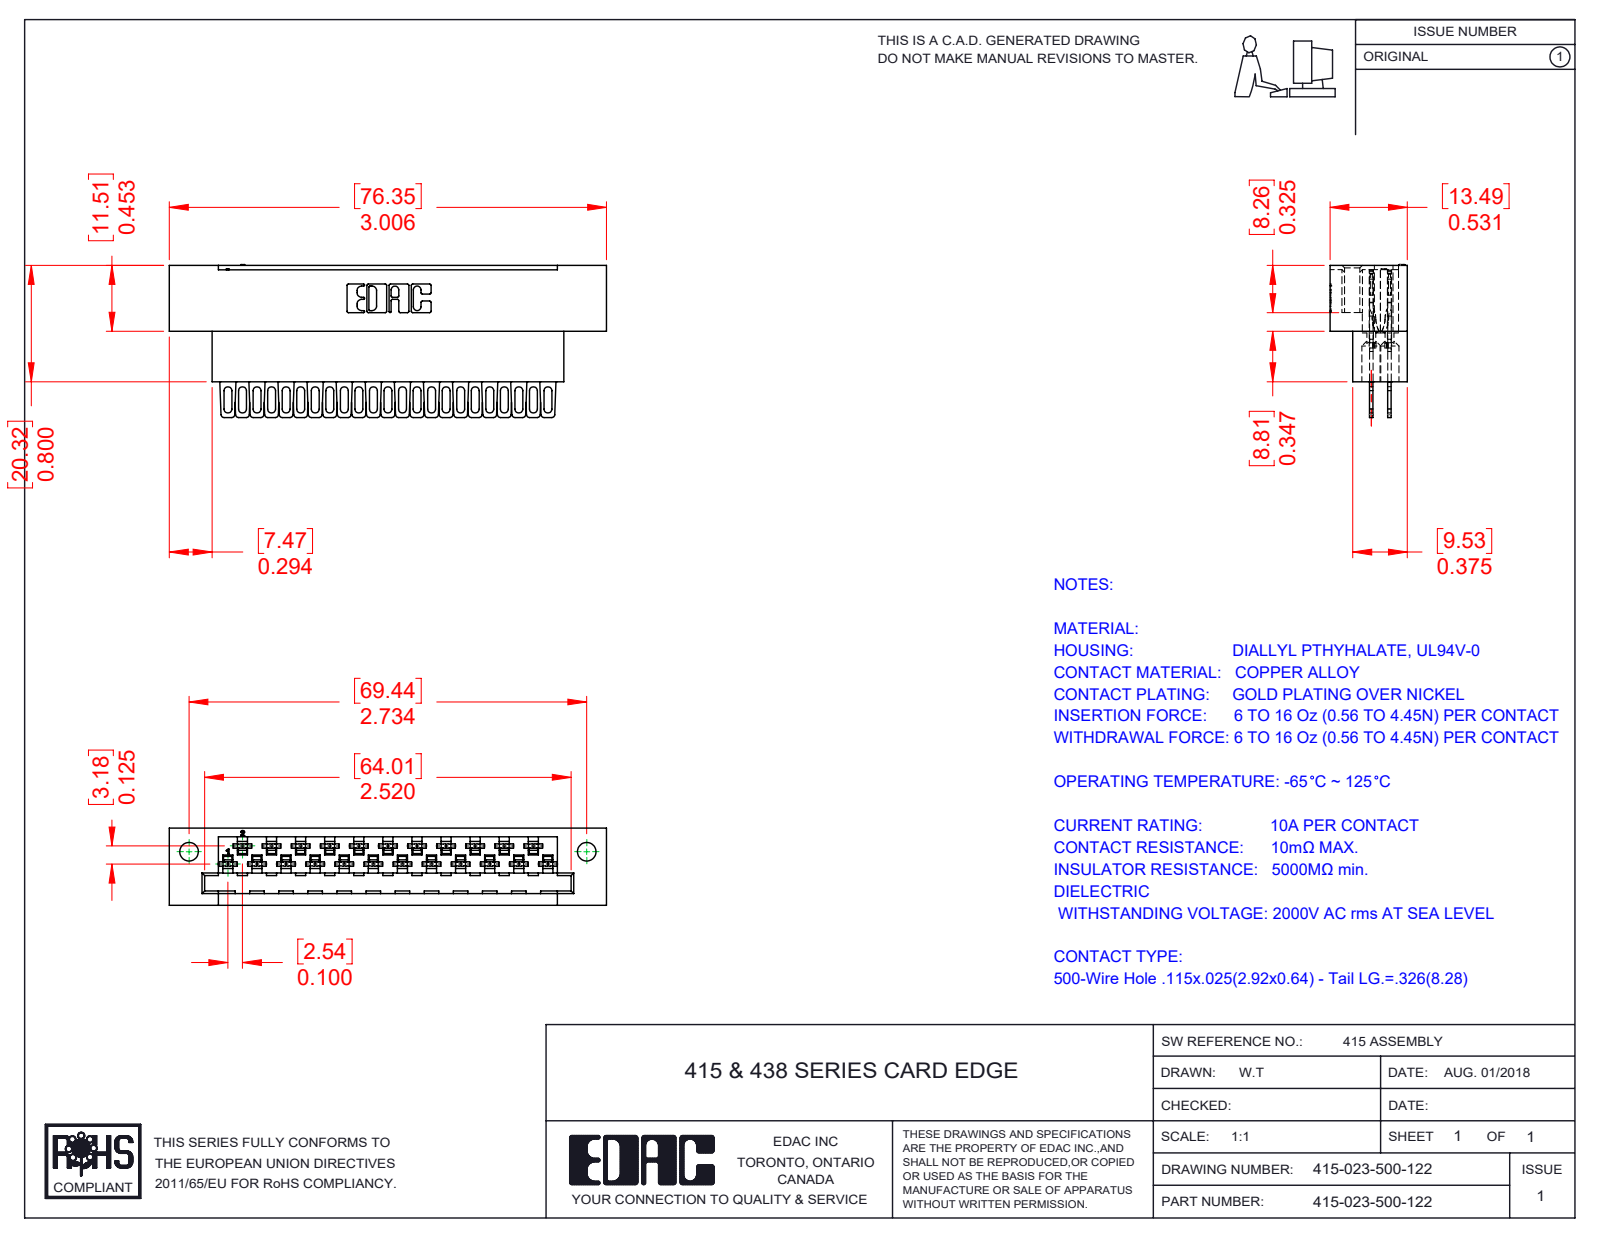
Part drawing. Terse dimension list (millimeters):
name: 516-290-001_500; 415-023-500-122; 415-210-001_415-210-023-122
written by: SolidWorks 2016 (CONFIG_CONTROL_DESIGN)
unit: mm
bodies: 24 solids, 2490 faces (1550 planar, 711 cylindrical, 229 other)
size: 76.35 × 26.68 × 13.49
volume: 12 450 mm³; area: 15 595 mm²
holes: 23× ⌀1.27, 23× ⌀3.3, 2× ⌀3.25
rounds: 92× R0.3, 92× R0.56, 46× R0.18, 46× R0.2, 46× R0.41, 46× R0.51, 46× R0.69, 46× R2.03
face distances: 3.18, 0.61, 13.49, 7.49, 1.27, 1.88, 6.61, 6.88, 6, 20.32
hole spacings: 5.08, 10.16, 15.24, 20.32, 25.4, 2.54, 4.06, 30.48
